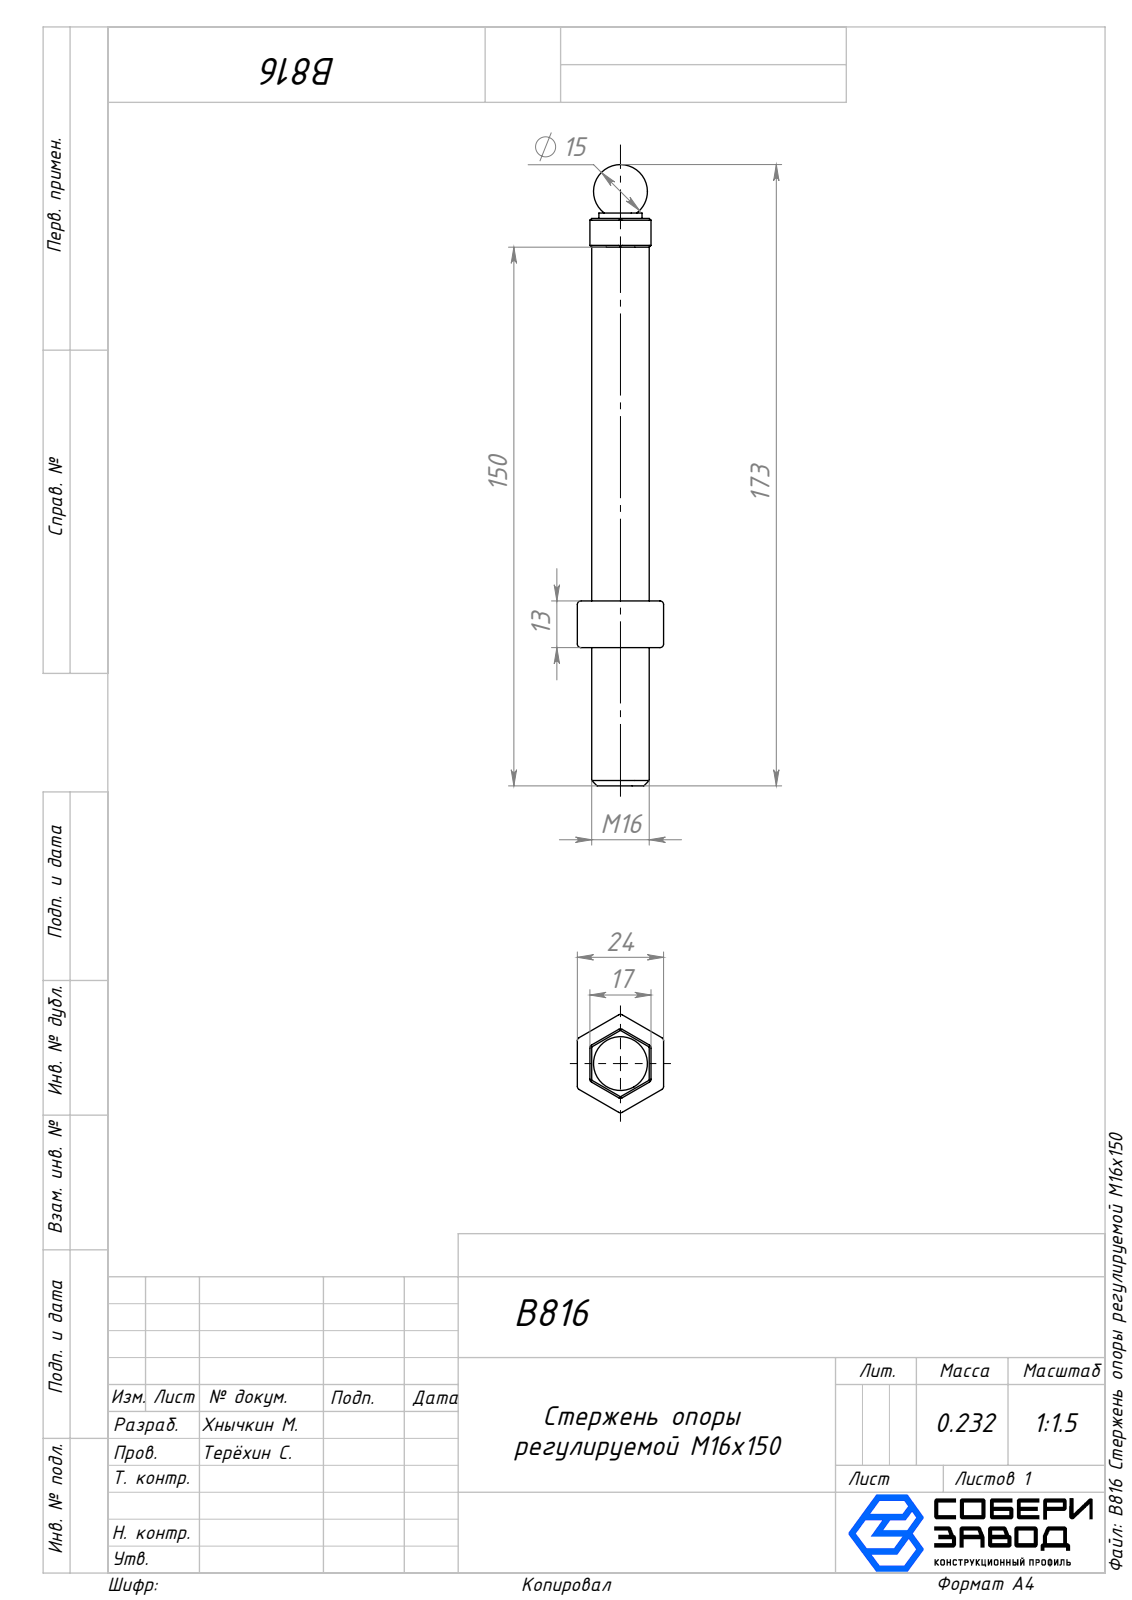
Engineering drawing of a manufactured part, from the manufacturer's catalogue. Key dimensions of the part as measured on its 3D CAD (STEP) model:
Part name (STEP PRODUCT): B816 Гайка М16_00; B816 Опора М16х150_00; B816 Стержень опоры регулируемой М16х150
STEP written by: SolidWorks 2025 (AUTOMOTIVE_DESIGN)
Units: millimetres
Bodies: 2 solids, 85 faces (35 planar, 30 cylindrical, 20 other)
Overall size (bounding box): 173 × 27.4 × 24
Volume: 38 378 mm³ · Surface area: 11 266 mm²
Round holes (diameter × count): ⌀14 ×1
Round bosses / shafts (diameter × count): ⌀16 ×1, ⌀12 ×1
Partial cylindrical surfaces — rounded edges, fillets, slot ends (radius × count): R1 ×24
Main face-to-face distances: 24, 3.5, 20.5, 13, 17, 38.5, 51.5, 158, 119.5, 106.5
